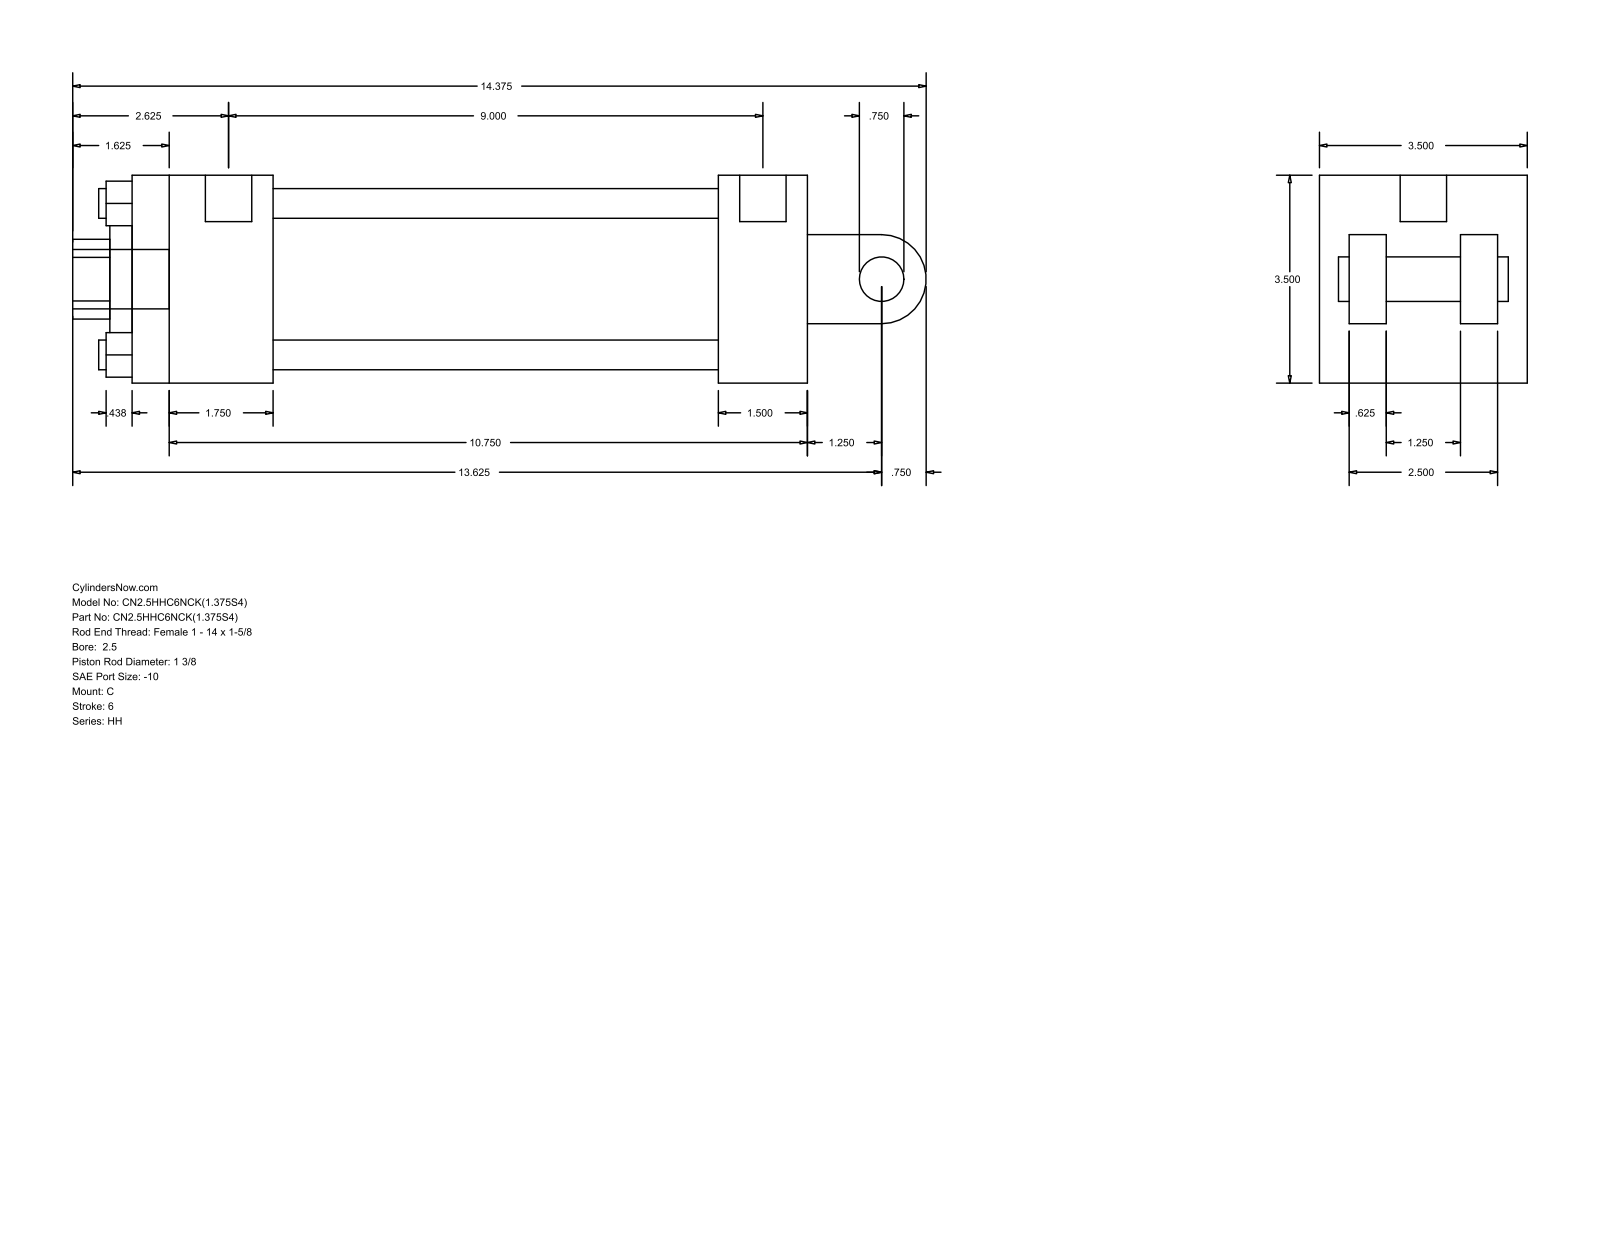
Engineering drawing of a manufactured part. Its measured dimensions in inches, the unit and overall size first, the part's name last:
Units: inches
Overall size (bounding box): 14.375 × 3.5 × 3.5
Round holes (diameter × count): ⌀0.5 ×4, ⌀0.219 ×2, ⌀0.781 ×1, ⌀1.375 ×1, ⌀2 ×1, ⌀2.875 ×1
Round bosses / shafts (diameter × count): ⌀0.219 ×2, ⌀1 ×1, ⌀0.781 ×1, ⌀0.75 ×1
Partial cylindrical surfaces — rounded edges, fillets, slot ends (radius × count): R0.672 ×1, R0.75 ×1
Main face-to-face distances: 3.5, 11.375, 2.5, 0.625, 0.5, 9.875, 1.5, 2.375, 7.5, 9
Hole centre spacings: 1.803, 2.55, 3.606, 0.063
Bodies: 0 solids, 99 faces (70 planar, 29 cylindrical, 0 other)
Part name (STEP PRODUCT): HH_C__0250_1.375
STEP written by: GSSL Pune (CONFIG_CONTROL_DESIGN)
